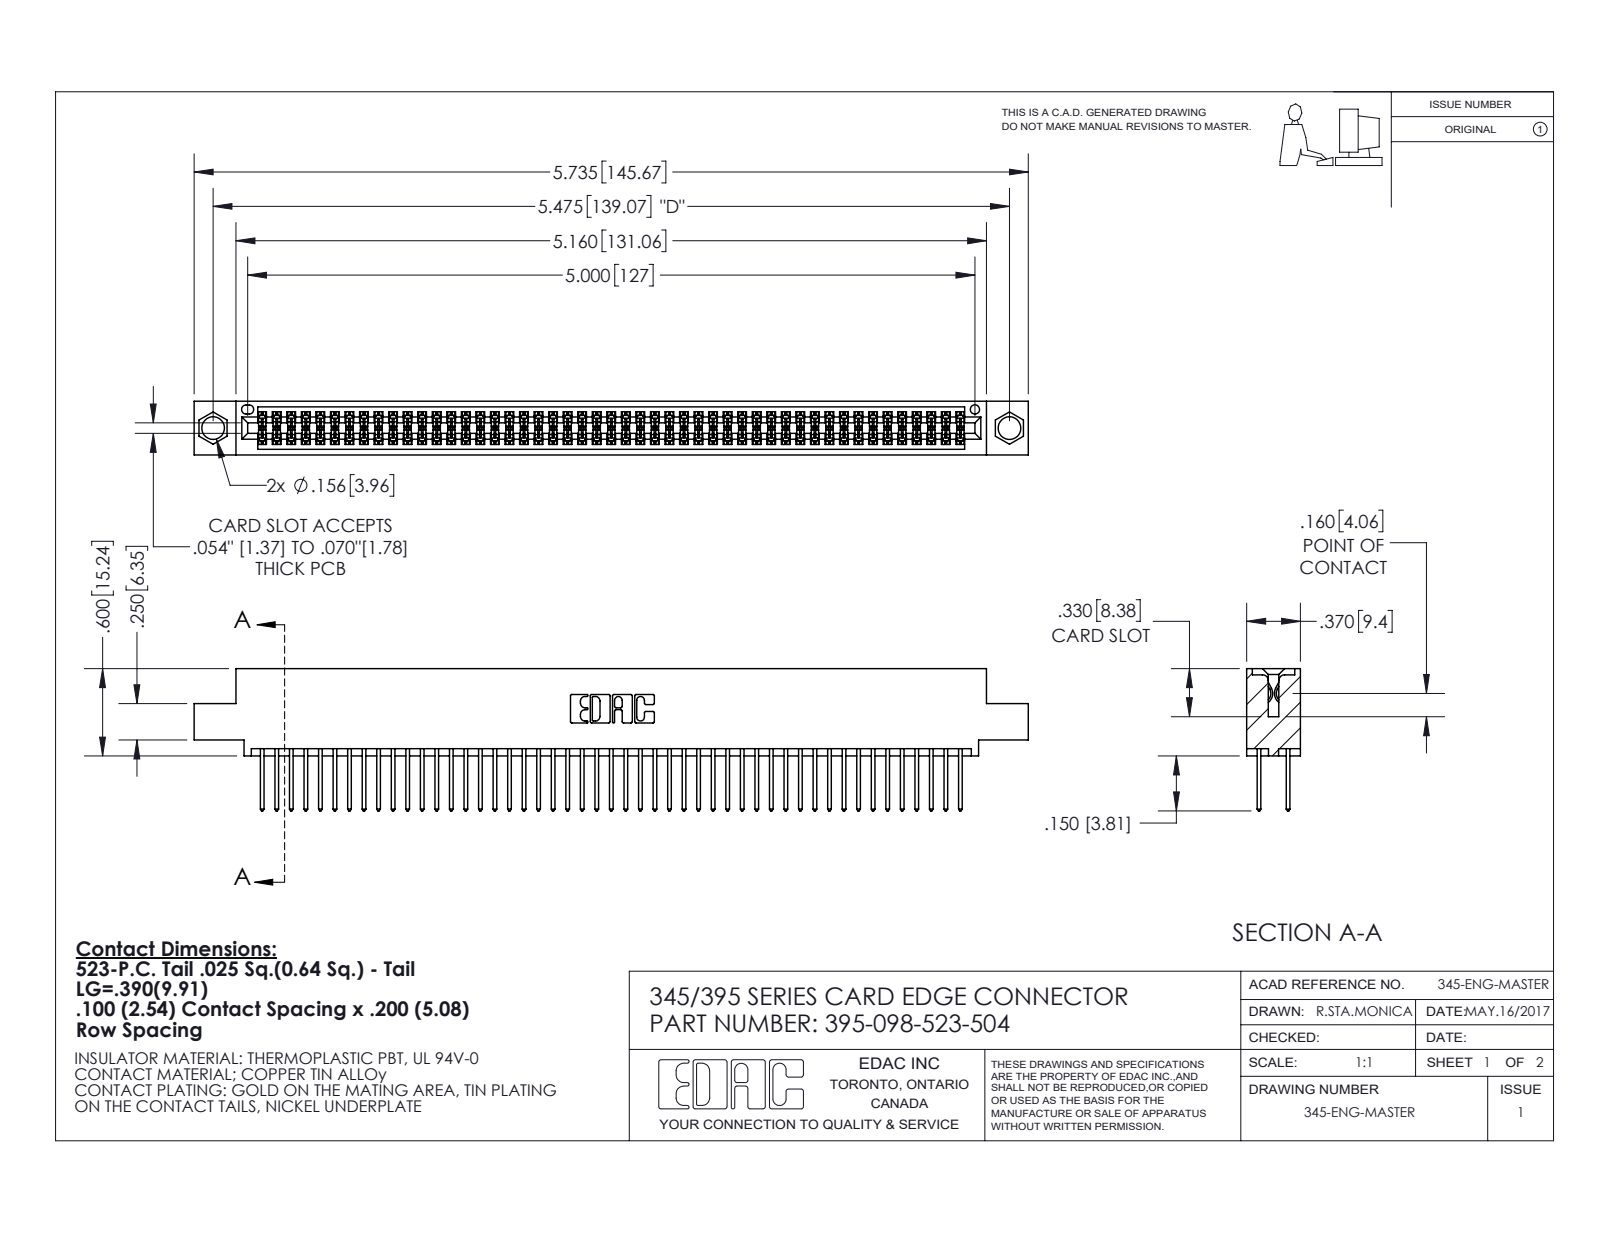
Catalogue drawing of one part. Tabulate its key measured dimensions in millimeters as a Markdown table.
| quantity | value |
| --- | --- |
| part name | 345-292-001_345-293-123; 345 Part_0.110 Offset - 0.156 Dia-TI; 395-098-523-504 |
| STEP written by | SolidWorks 2020 (CONFIG_CONTROL_DESIGN) |
| units | millimeters |
| bodies | 99 solids, 5044 faces (3332 planar, 1712 cylindrical, 0 other) |
| overall size | 145.7 × 24.8 × 9.4 |
| volume | 14 200 mm³ |
| surface area | 22 030 mm² |
| round holes (diameter × count) | 4 × 2, 1.6 × 1 |
| partial cylindrical surfaces (radius × count) | 0.2 × 196, 0.3 × 98, 0.3 × 22, 0.2 × 6, 0.8 × 6, 0.7 × 3, 0.4 × 2, 0.5 × 2 |
| main face-to-face distances | 1.8, 7.6, 5.1, 2.5, 6.9, 0.6, 9.4, 5.7, 4.4, 3.8 |
| hole center spacings | 6.9, 133.1, 139.1 |
